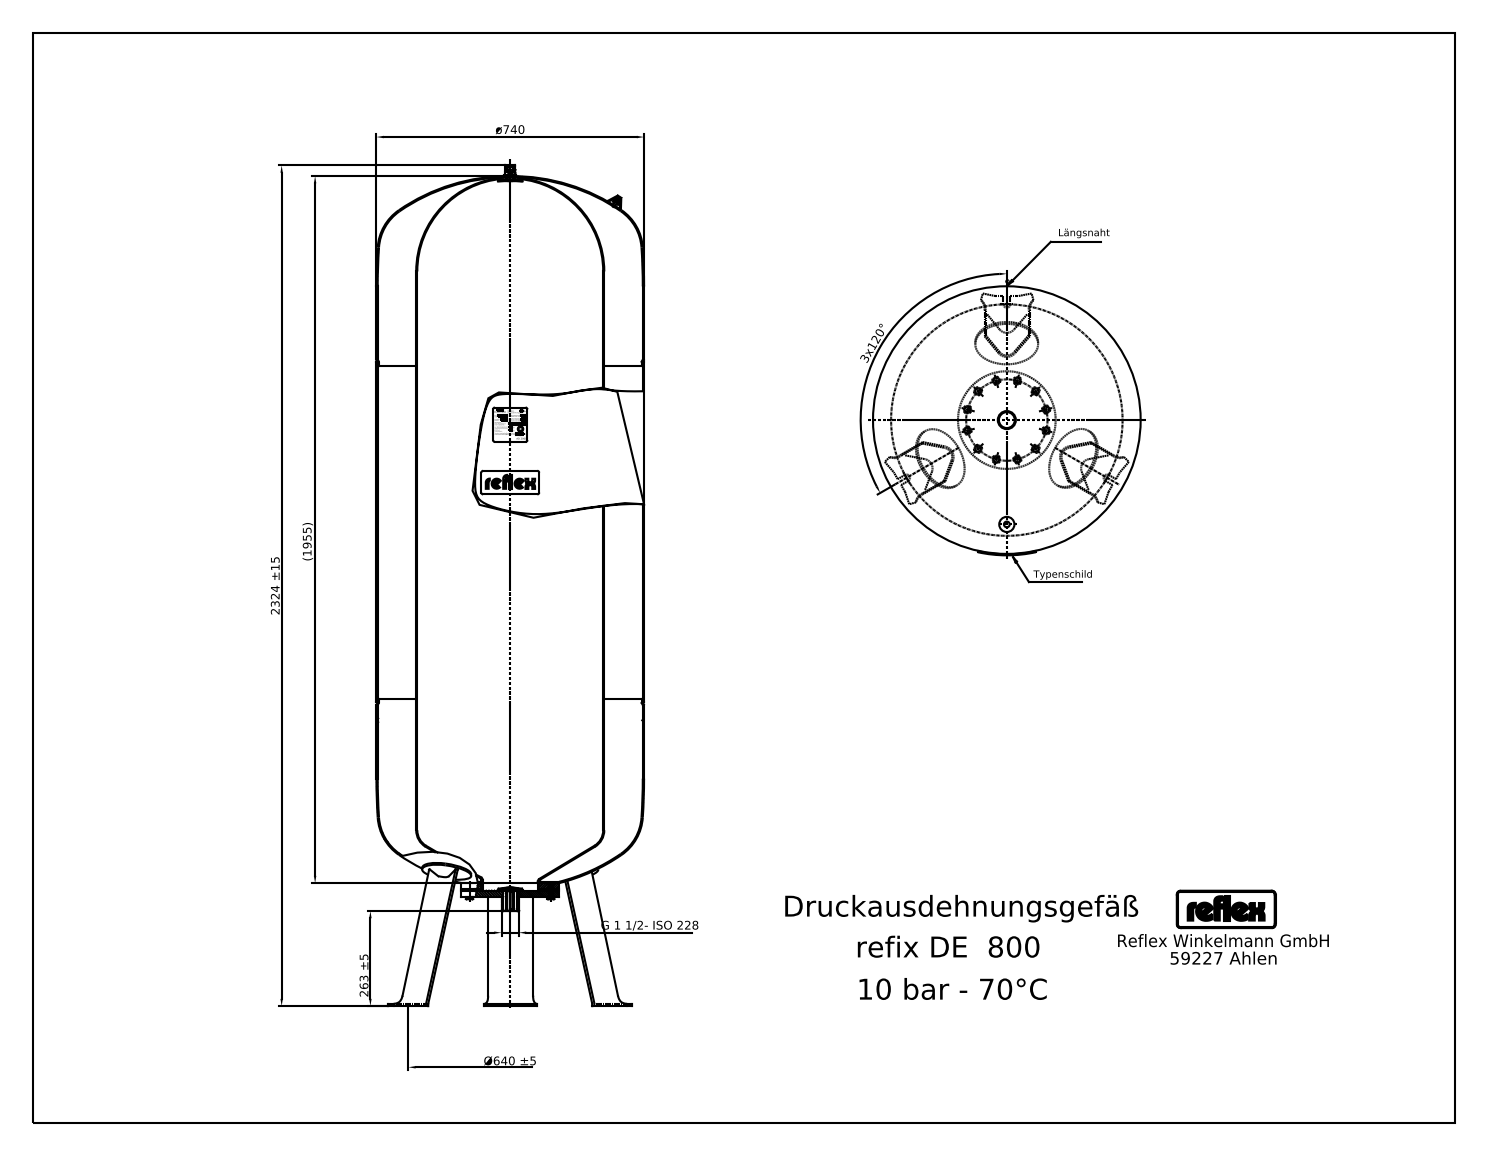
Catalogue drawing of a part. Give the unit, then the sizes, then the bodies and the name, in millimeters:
Units: millimetres
Overall size (bounding box): 2324 × 740 × 740
Round holes (diameter × count): ⌀14.1 ×1, ⌀160 ×1
Round bosses / shafts (diameter × count): ⌀16 ×13, ⌀740 ×1, ⌀270 ×1, ⌀48.3 ×1, ⌀34 ×1, ⌀17.1 ×1, ⌀9 ×1, ⌀6 ×1
Partial cylindrical surfaces — rounded edges, fillets, slot ends (radius × count): R25 ×18, R5.62 ×4, R2.25 ×3, R9 ×3, R3.84 ×2, R6.75 ×2, R9.27 ×2, R9.4 ×2
Main face-to-face distances: 1592, 16, 21, 195, 1787, 5.97, 5.89, 211, 1803, 37
Volume: 795 300 000 mm³ · Surface area: 7 558 000 mm²
Bodies: 20 solids, 441 faces (221 planar, 123 cylindrical, 97 other)
STEP written by: Mechanical Desktop 2008 (CONFIG_CONTROL_DESIGN)
